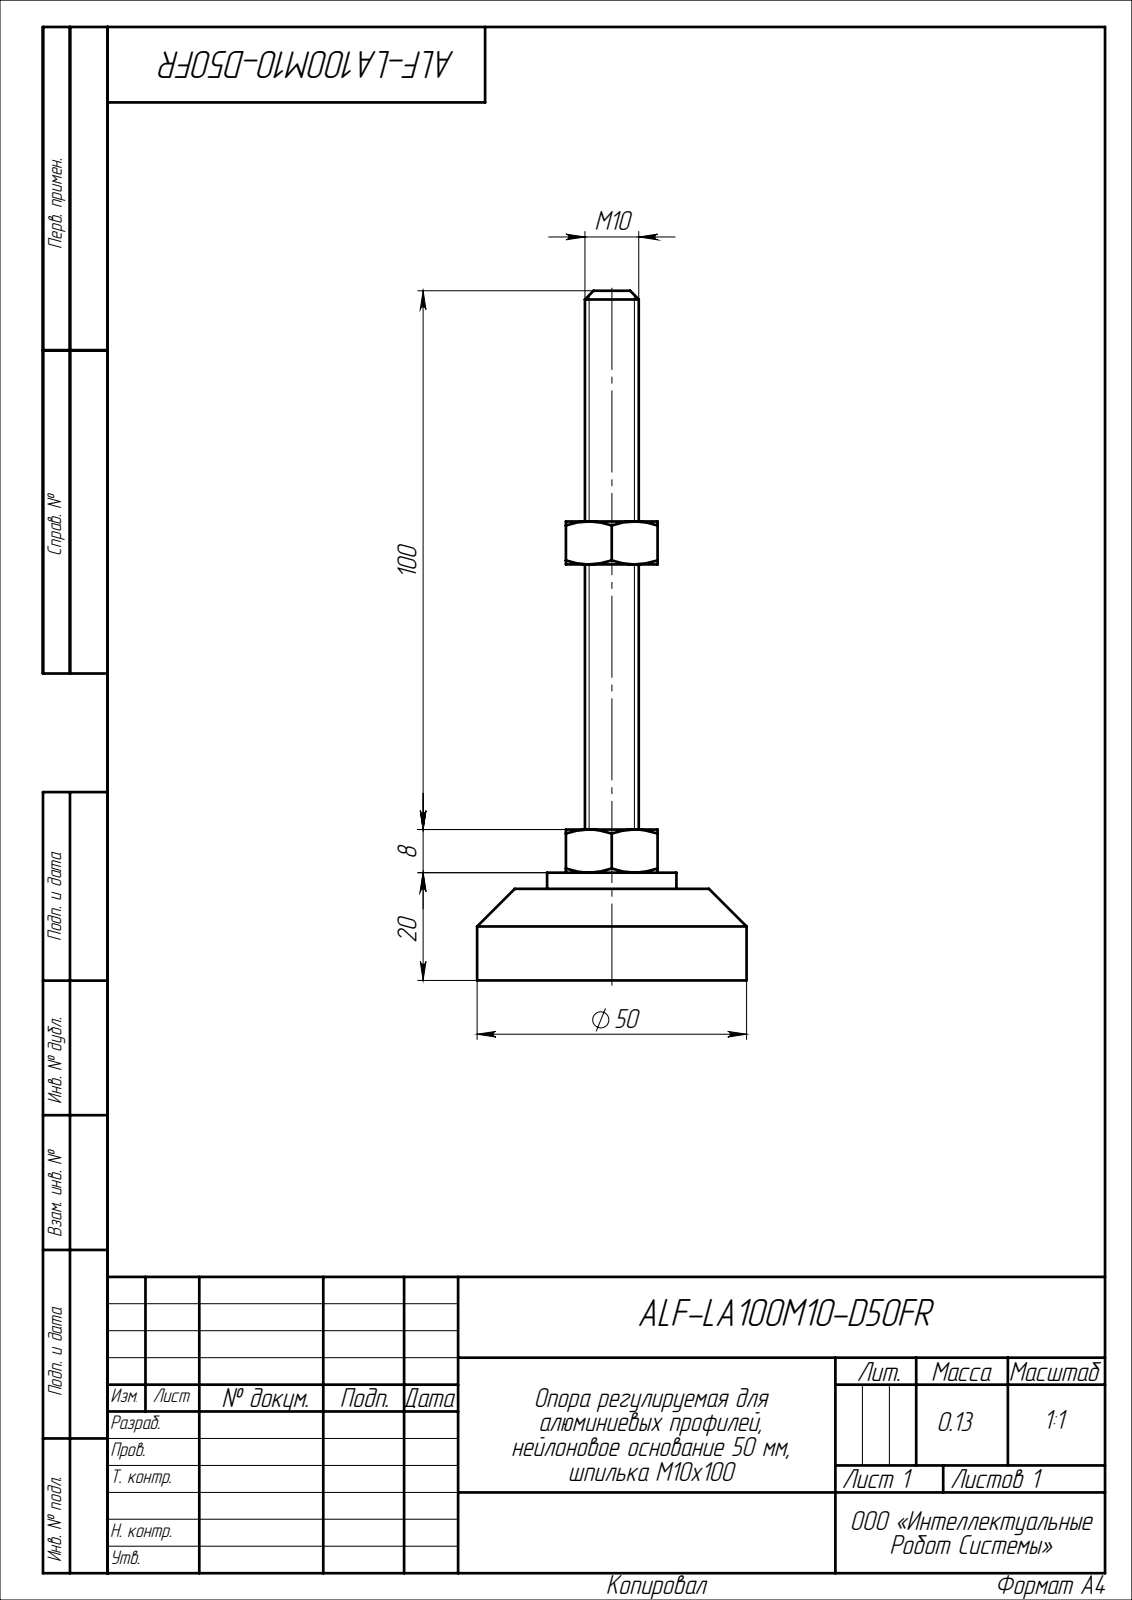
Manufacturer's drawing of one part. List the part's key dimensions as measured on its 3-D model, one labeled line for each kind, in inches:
Part name (STEP PRODUCT): ALF-LA100M10-D50FR
STEP written by: SolidWorks 2022 (CONFIG_CONTROL_DESIGN)
Units: inches
Bodies: 1 solid, 55 faces (19 planar, 8 cylindrical, 28 other)
Overall size (bounding box): 5.039 × 1.969 × 1.969
Volume: 2.589 in³ · Surface area: 15.9 in²
Round bosses / shafts (diameter × count): ⌀1.969 ×1, ⌀0.945 ×1, ⌀0.394 ×1
Main face-to-face distances: 0.669, 0.315, 2.252, 0.787, 0.118, 1.102, 0.433, 3.354, 2.685, 2.567
